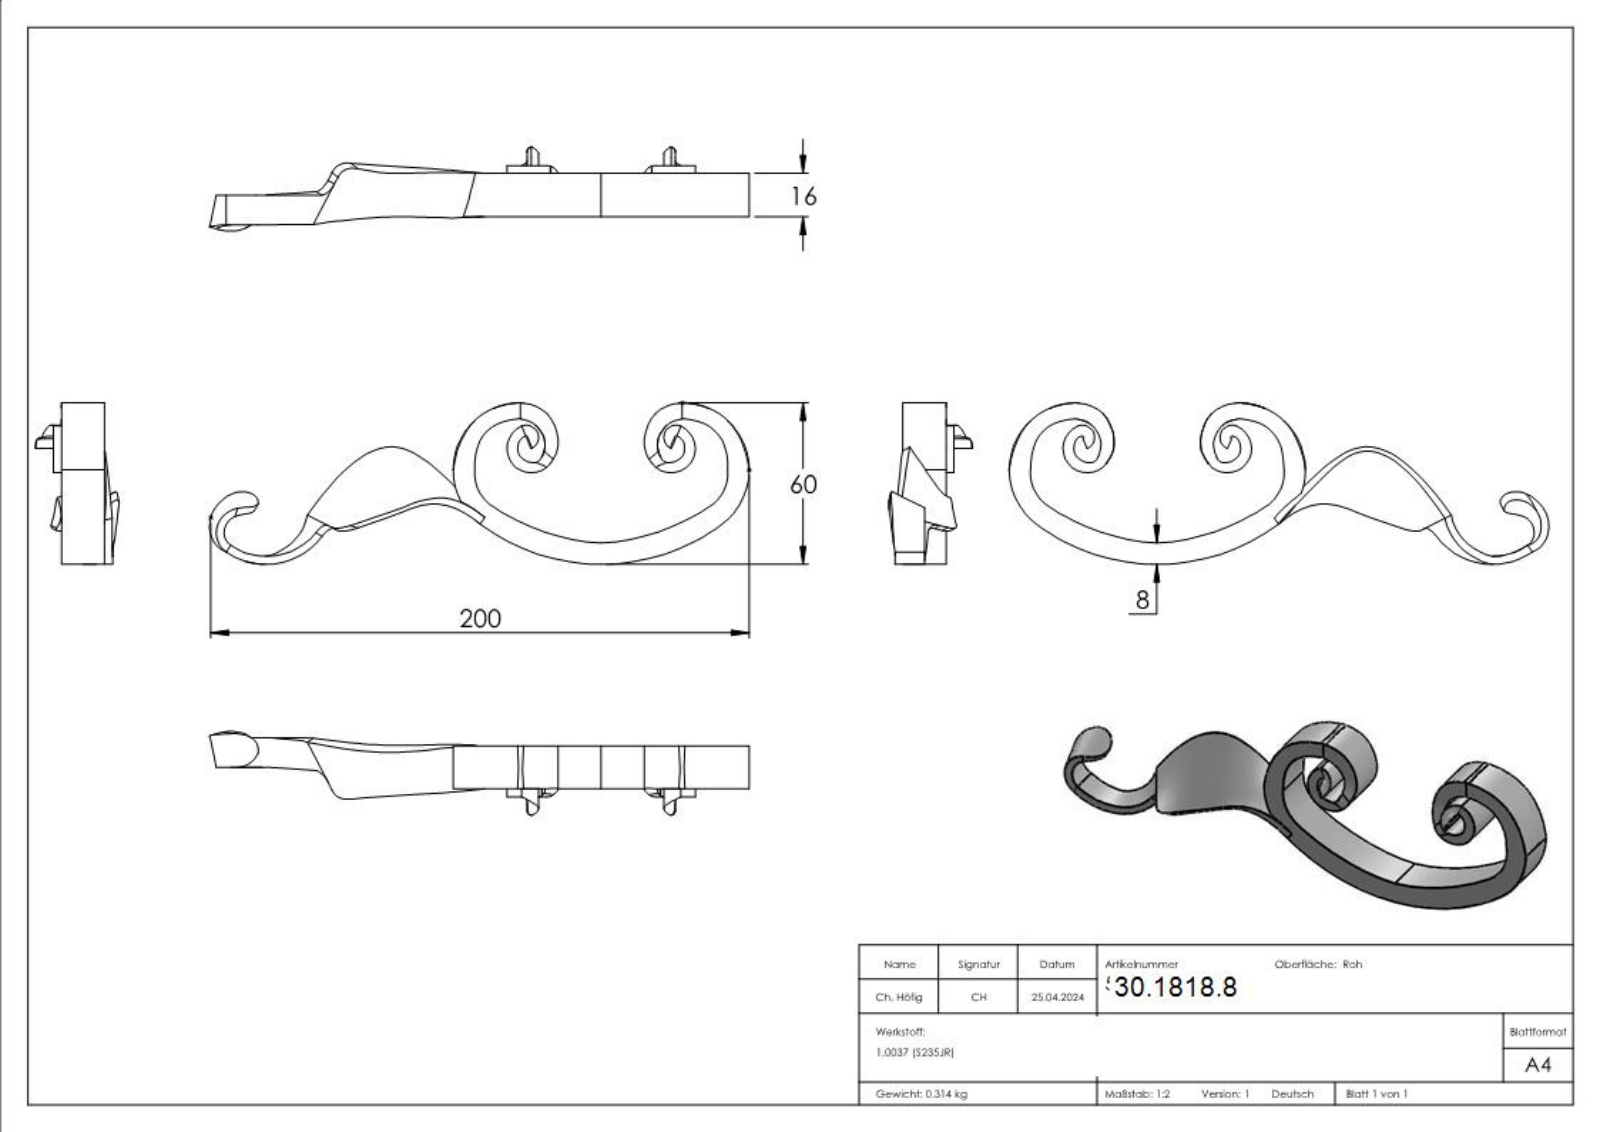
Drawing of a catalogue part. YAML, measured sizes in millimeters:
part_name: "5008"
step_written_by: "SolidWorks 2018 (CONFIG_CONTROL_DESIGN)"
units: millimeters
bodies: {solids: 1, faces: 232, planar: 88, cylindrical: 0, other: 144}
overall_size: [200.45, 60.04, 31.17]
volume: 40284
surface_area: 20133
face_to_face_distances: [16, 19, 3, 0.75, 1.78, 1.21, 0.67, 0.82, 1.96, 0.79]
